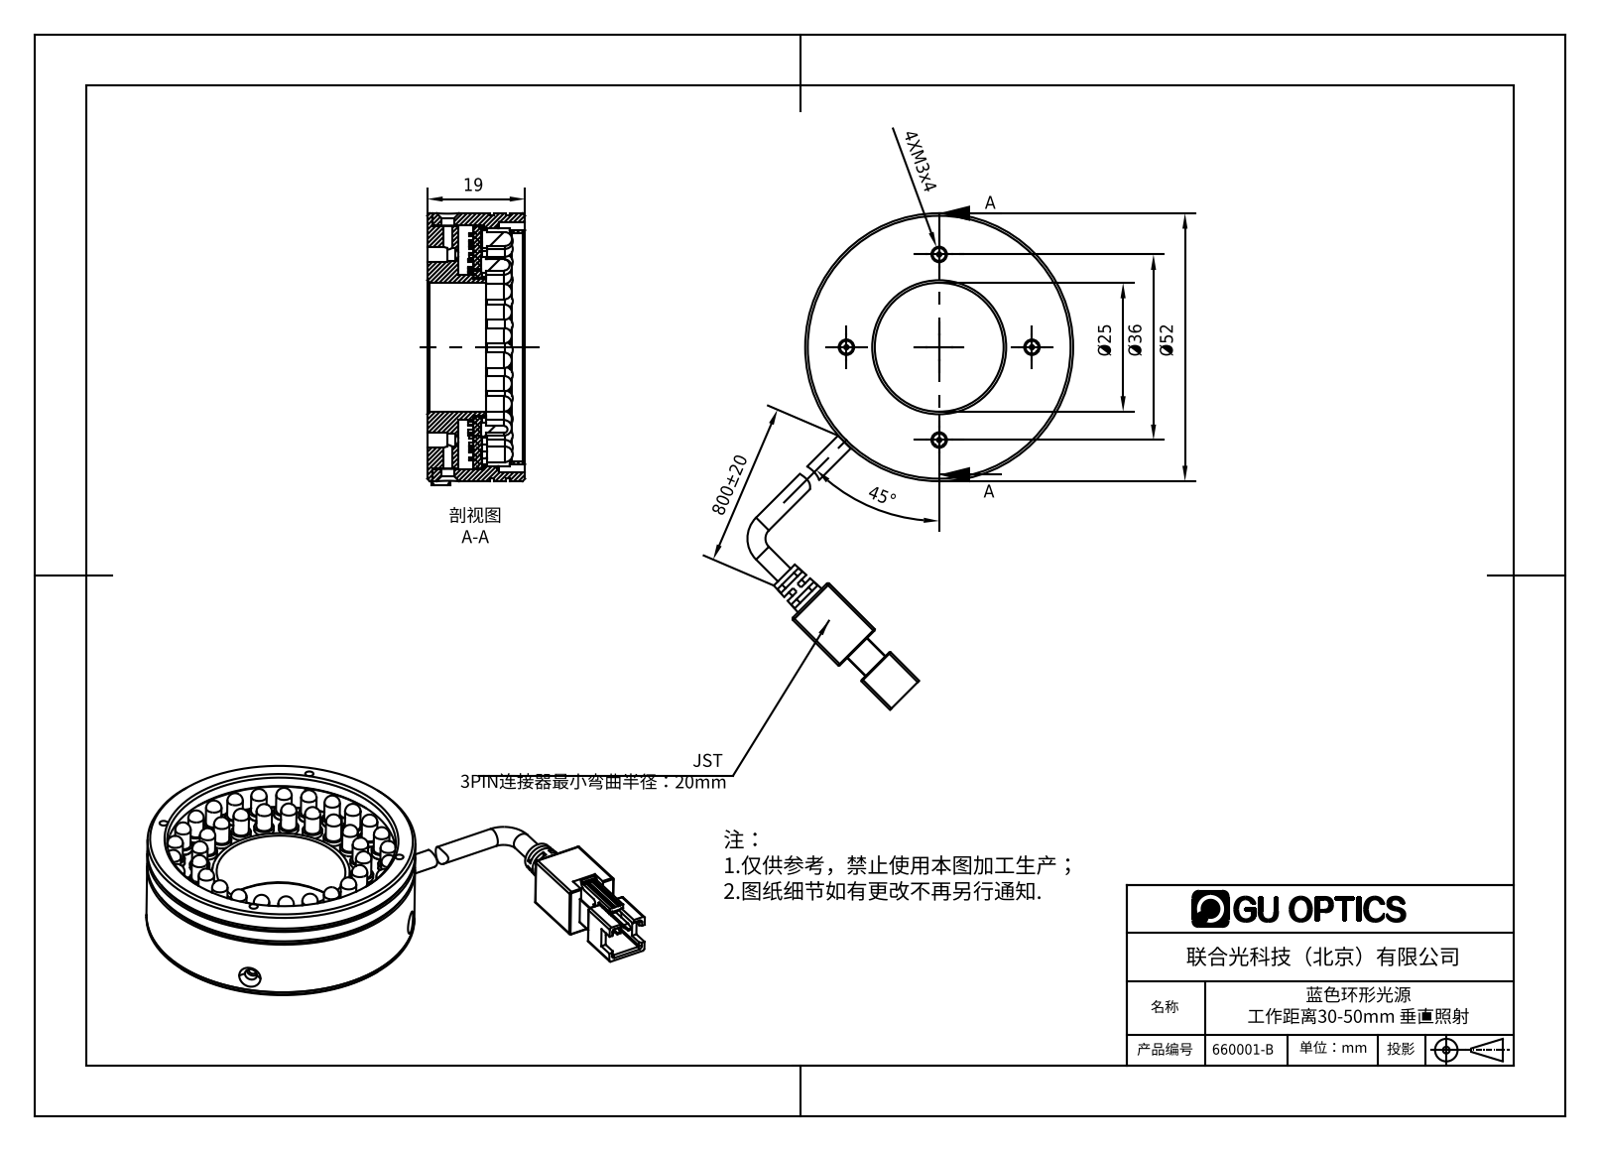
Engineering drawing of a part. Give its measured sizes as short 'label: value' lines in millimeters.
name: 660001-B
written by: SolidWorks 2016 (AUTOMOTIVE_DESIGN)
unit: mm
bodies: 53 solids, 1320 faces (770 planar, 437 cylindrical, 113 other)
size: 96.36 × 63.22 × 21.35
volume: 21 232 mm³; area: 21 563 mm²
holes: 48× ⌀3.8, 6× ⌀1.6, 4× ⌀2.5, 4× ⌀3, 2× ⌀2.4, 1× ⌀25, 1× ⌀27, 1× ⌀44.4, 1× ⌀46.2, 1× ⌀47.2
bosses: 48× ⌀3, 2× ⌀3.5, 1× ⌀52, 1× ⌀51, 1× ⌀47.1, 1× ⌀47, 1× ⌀28, 1× ⌀26.7
rounds: 15× R0.1, 13× R0.2, 12× R0.4, 1× R0.3, 1× R0.68, 1× R1.4, 1× R1.75, 1× R8
face distances: 3, 1, 9, 6, 5, 4.6, 1.6, 10.6, 8, 10
hole spacings: 16, 4.77, 25.02, 31.91, 9.43, 13.88, 27.71, 18.03
